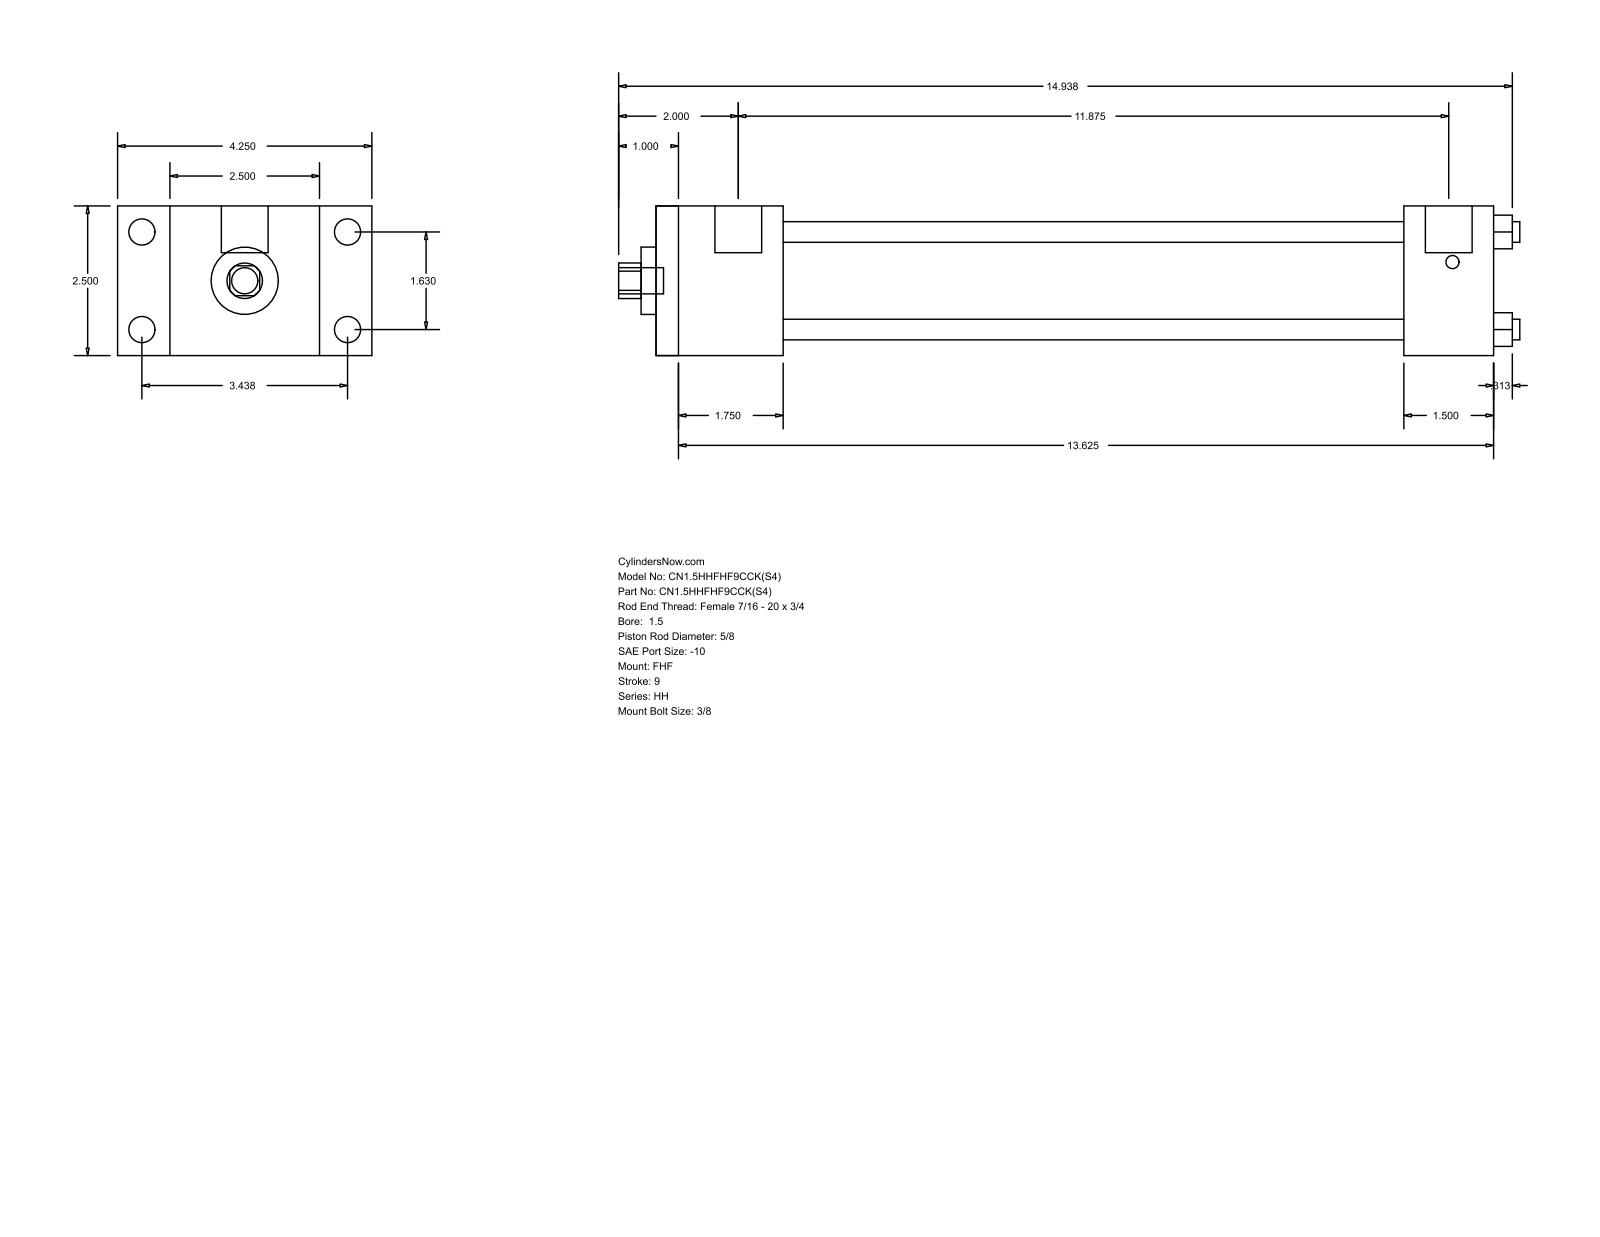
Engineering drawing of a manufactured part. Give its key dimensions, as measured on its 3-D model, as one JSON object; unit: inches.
{"part_name": "HH_FHF__0150_0.625", "step_written_by": "GSSL Pune (CONFIG_CONTROL_DESIGN)", "units": "inches", "bodies": {"solids": 0, "faces": 88, "planar": 60, "cylindrical": 28, "other": 0}, "overall_size": [15.063, 4.25, 2.5], "round_holes": [[0.345, 4], [0.625, 1], [1.125, 1], [1.75, 1]], "round_bosses_or_shafts": [[0.438, 4], [0.219, 4], [0.781, 2], [0.437, 1]], "partial_cylinders_radius": [[0.297, 1]], "face_to_face_distances": [2.5, 0.875, 3.375, 2.125, 4.25, 14, 11.875, 1.5, 12.5, 10.375], "hole_center_spacings": [1.152, 1.63, 2.305]}
